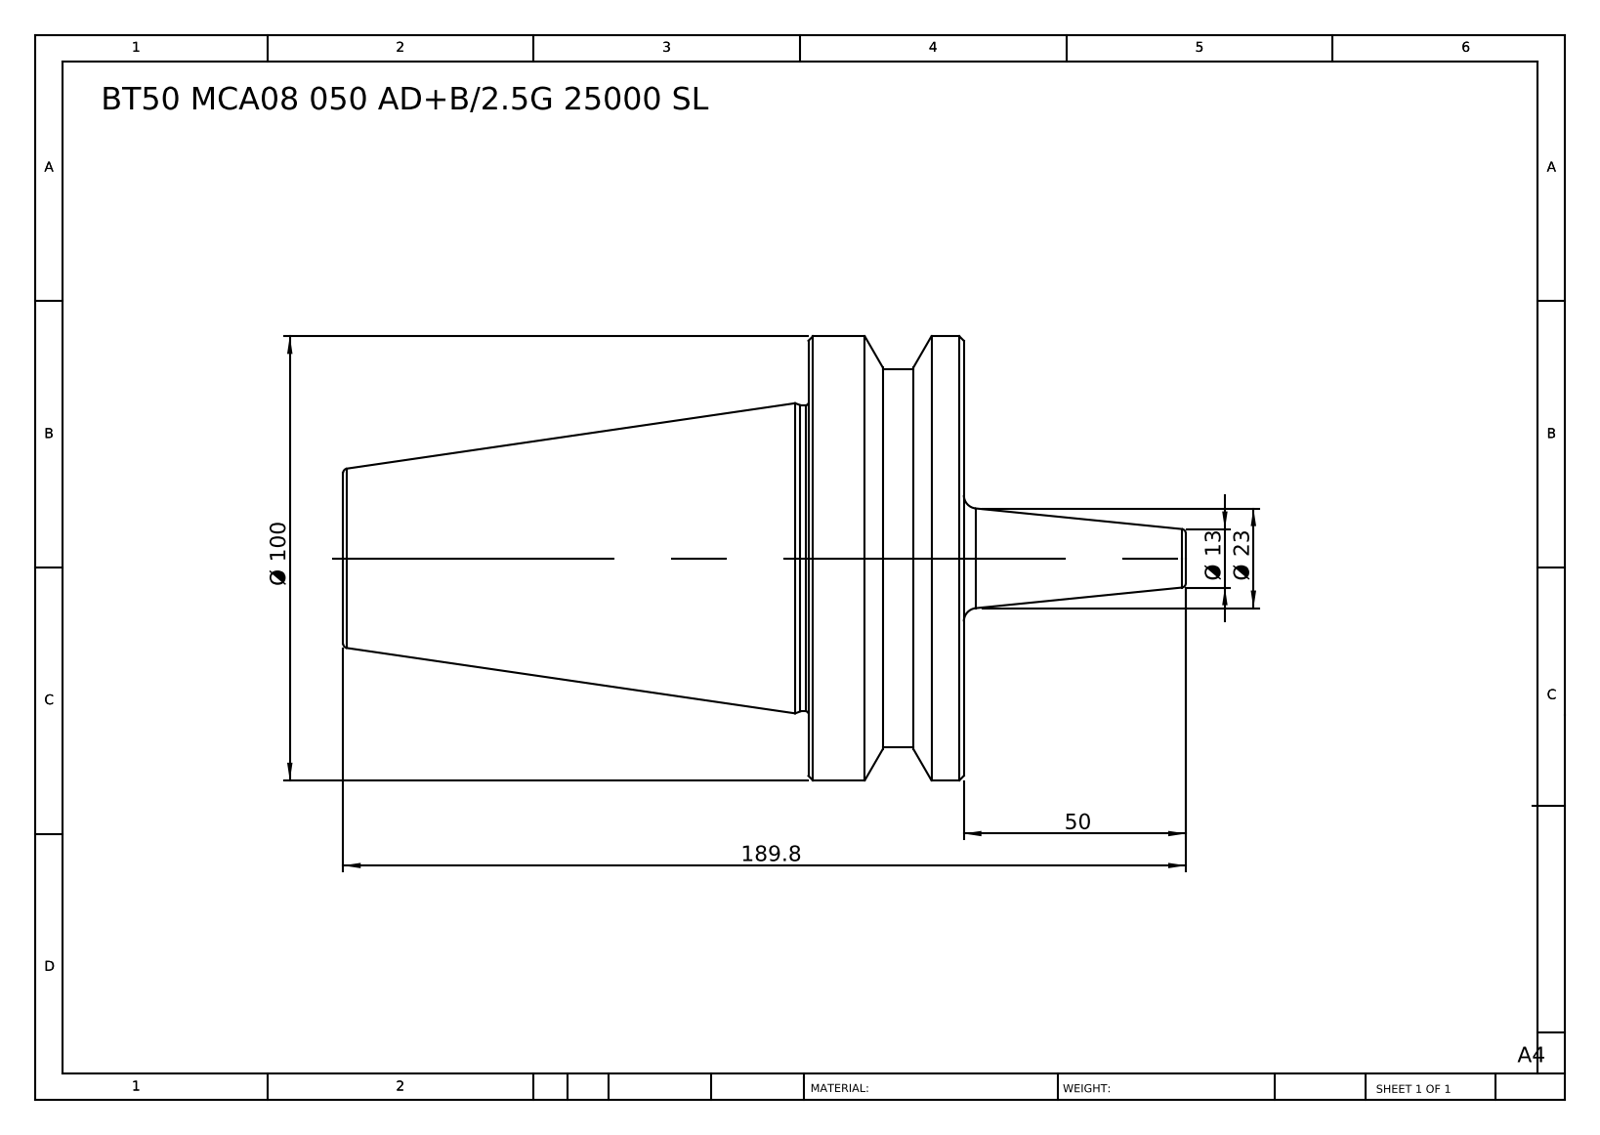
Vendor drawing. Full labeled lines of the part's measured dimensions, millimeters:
Part name (STEP PRODUCT): BT50 MCA08 050 AD+B-2.5G 25000 SL
STEP written by: SolidWorks 2014 (CONFIG_CONTROL_DESIGN)
Units: millimetres
Bodies: 1 solid, 36 faces (6 planar, 8 cylindrical, 22 other)
Overall size (bounding box): 189.8 × 100 × 100
Volume: 523 210 mm³ · Surface area: 46 838 mm²
Round bosses / shafts (diameter × count): ⌀100 ×1, ⌀85 ×1, ⌀69 ×1
Main face-to-face distances: 35, 139.8, 104.8, 11.3, 23.7, 128.5, 18.3, 7, 16.7, 121.5
